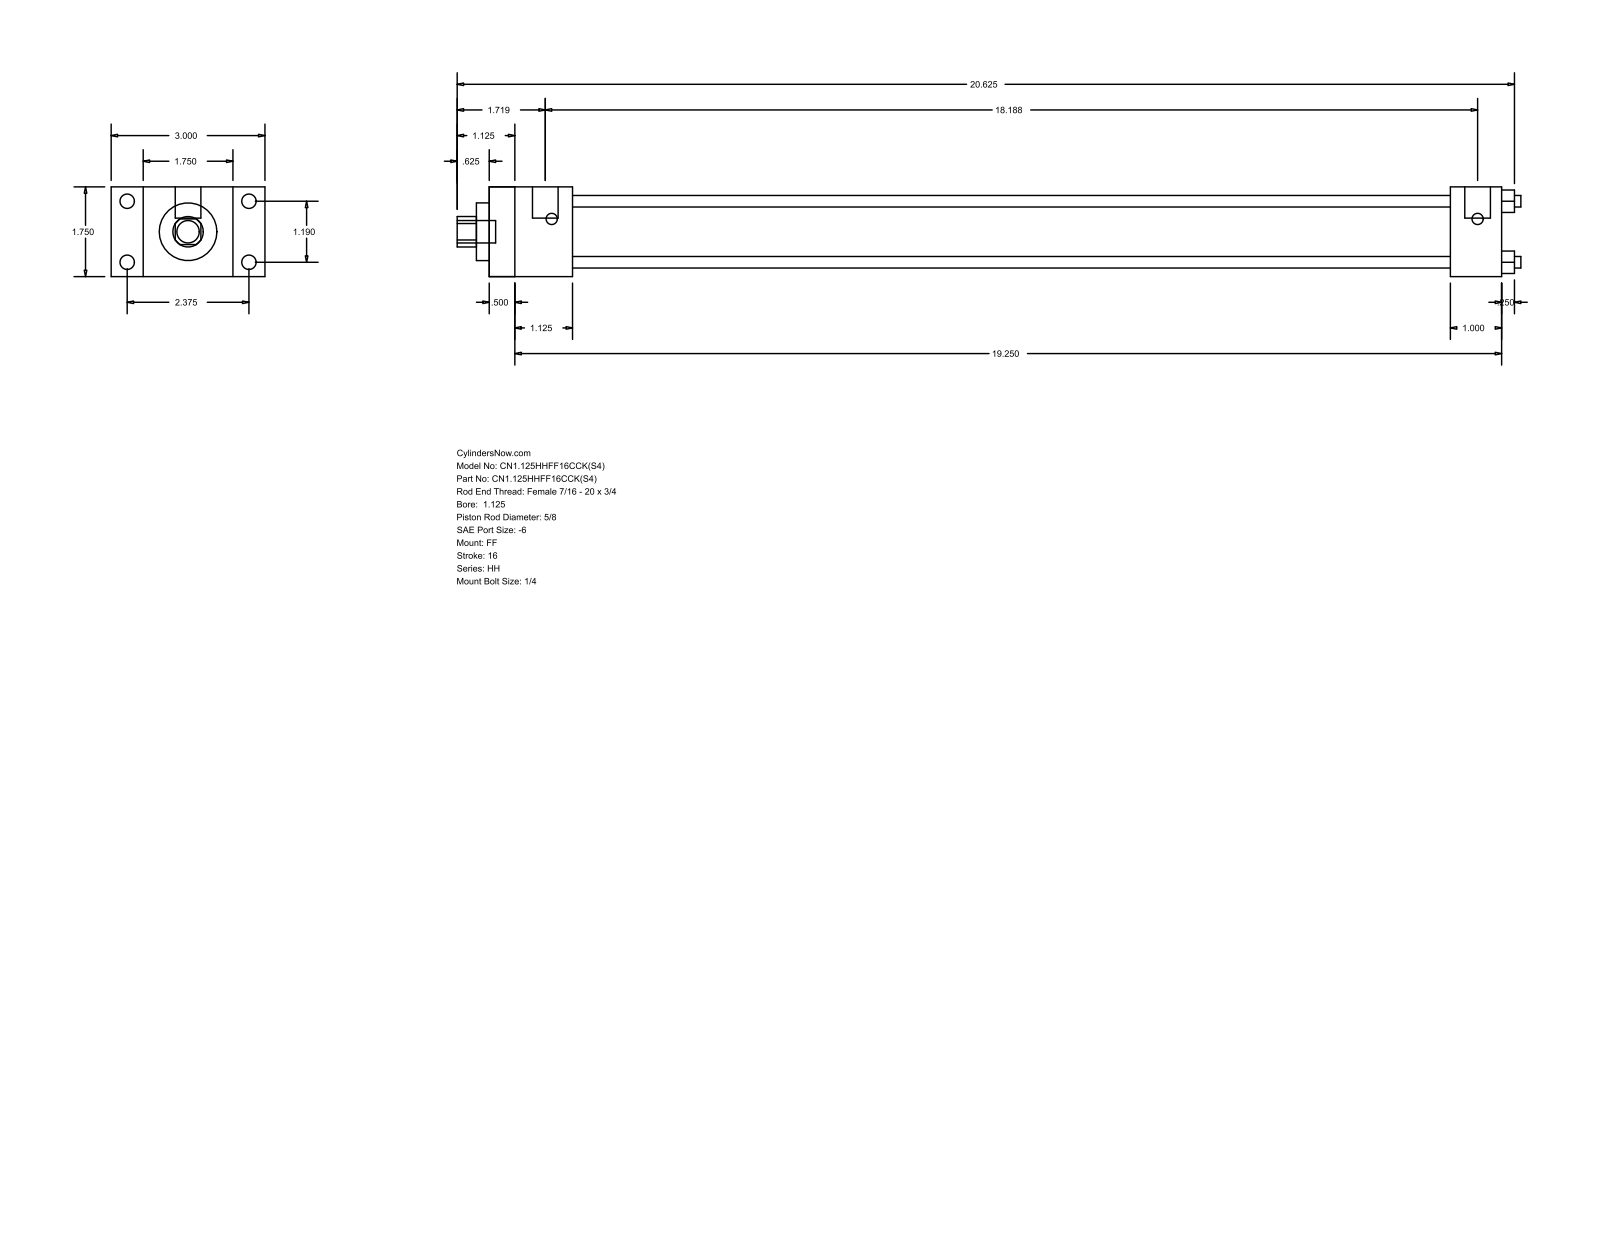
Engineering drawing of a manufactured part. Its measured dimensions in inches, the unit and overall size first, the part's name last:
Units: inches
Overall size (bounding box): 20.75 × 3 × 1.75
Round holes (diameter × count): ⌀0.225 ×4, ⌀0.625 ×1, ⌀1.125 ×1, ⌀1.375 ×1
Round bosses / shafts (diameter × count): ⌀0.281 ×4, ⌀0.219 ×4, ⌀0.5 ×2, ⌀0.437 ×1
Partial cylindrical surfaces — rounded edges, fillets, slot ends (radius × count): R0.297 ×1
Main face-to-face distances: 1.75, 19.75, 0.5, 19.25, 0.625, 2.375, 1.125, 1.625, 18.75, 18.25
Hole centre spacings: 0.841, 1.19, 1.683
Bodies: 0 solids, 92 faces (64 planar, 28 cylindrical, 0 other)
Part name (STEP PRODUCT): HH_FF__0112_0.625
STEP written by: GSSL Pune (CONFIG_CONTROL_DESIGN)
